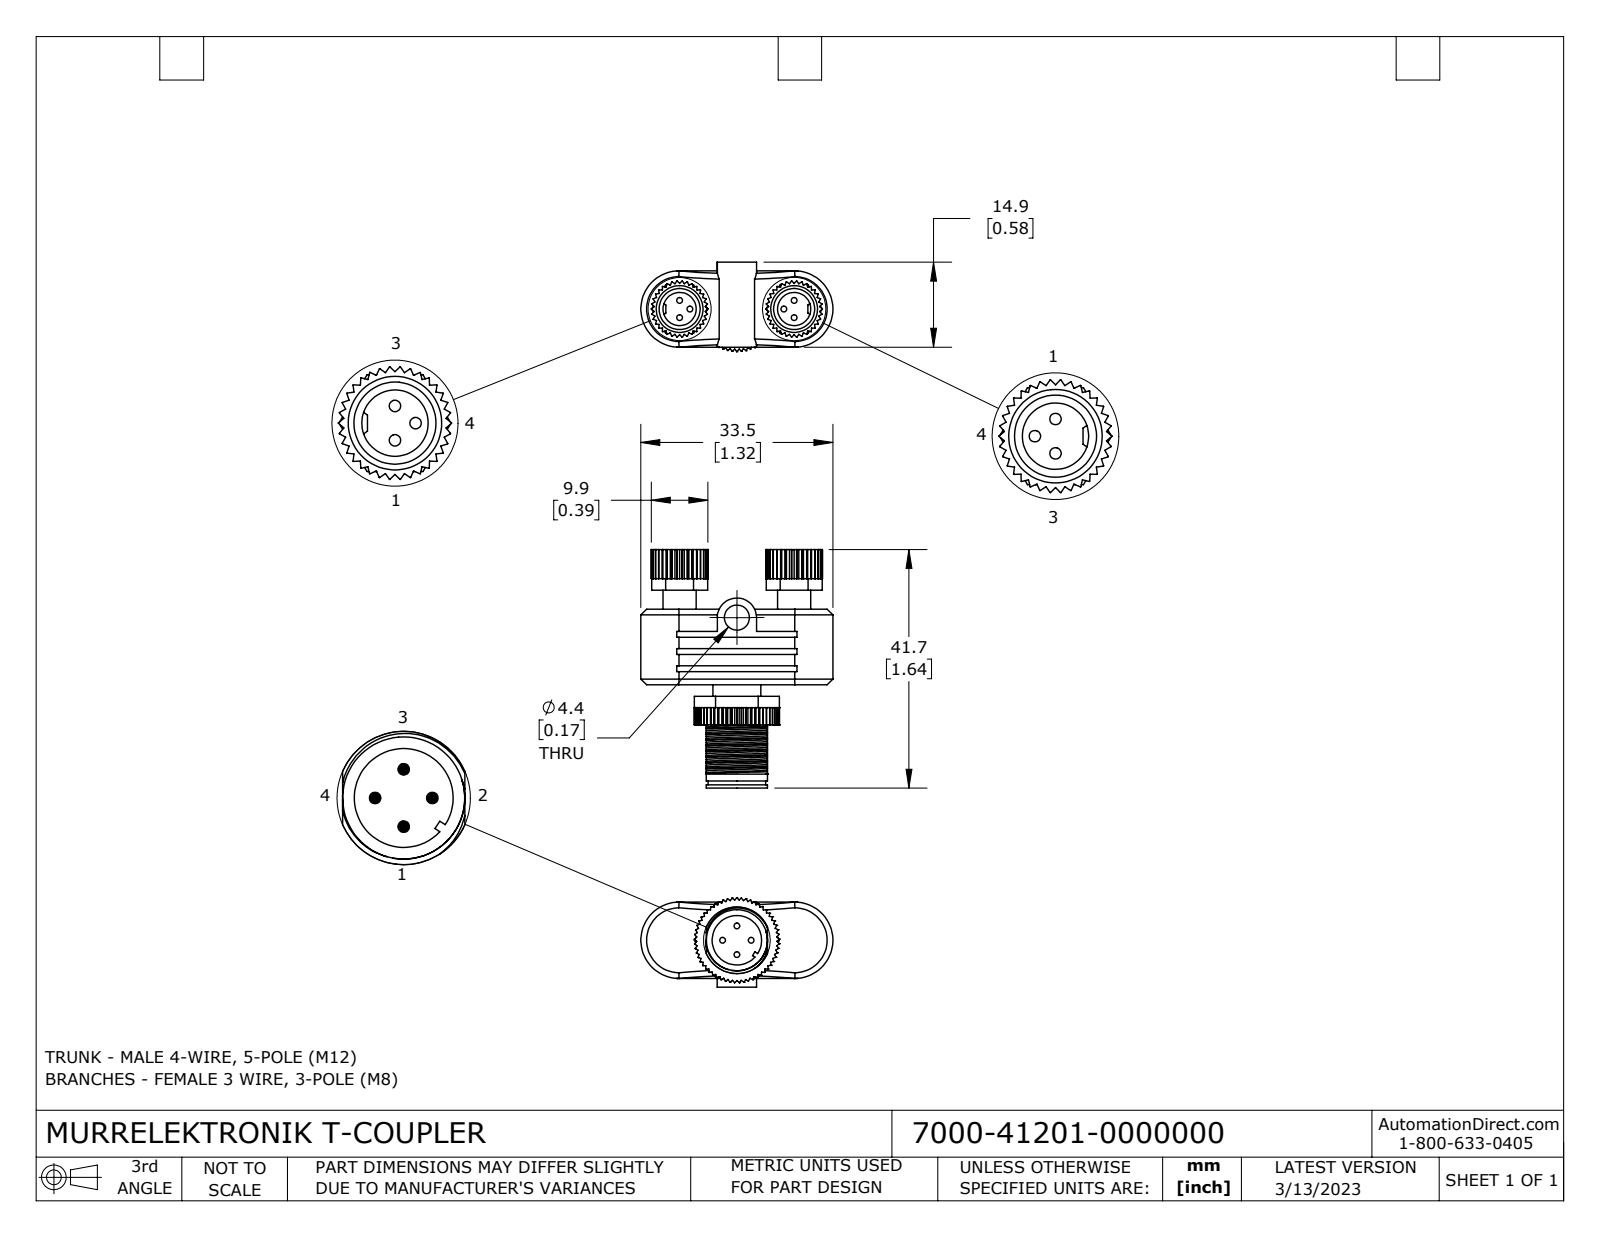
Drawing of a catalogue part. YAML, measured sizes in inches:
part_name: "7000-41201-0000000"
step_written_by: "SolidWorks 2021 (CONFIG_CONTROL_DESIGN)"
units: inches
bodies: {solids: 1, faces: 740, planar: 440, cylindrical: 212, other: 88}
overall_size: [1.64, 1.32, 0.615]
volume: 0.463
surface_area: 7.789
round_holes:
  - {diameter: 0.039, count: 6}
  - {diameter: 0.282, count: 2}
  - {diameter: 0.172, count: 1}
  - {diameter: 0.34, count: 1}
round_bosses_or_shafts:
  - {diameter: 0.039, count: 4}
  - {diameter: 0.228, count: 2}
  - {diameter: 0.42, count: 1}
  - {diameter: 0.396, count: 1}
  - {diameter: 0.33, count: 1}
partial_cylinders:
  - {radius: 0.194, count: 2}
  - {radius: 0.263, count: 2}
  - {radius: 0.135, count: 1}
  - {radius: 0.229, count: 1}
  - {radius: 0.293, count: 1}
  - {radius: 4.157, count: 1}
  - {radius: 4.158, count: 1}
face_to_face_distances: [0.52, 0.079, 0.25, 0.197, 1.008, 0.249, 0.598, 0.13, 0.41, 0.93]
hole_center_spacings: [0.059, 0.092, 0.398, 0.719, 0.79, 0.787, 0.071, 0.118]
